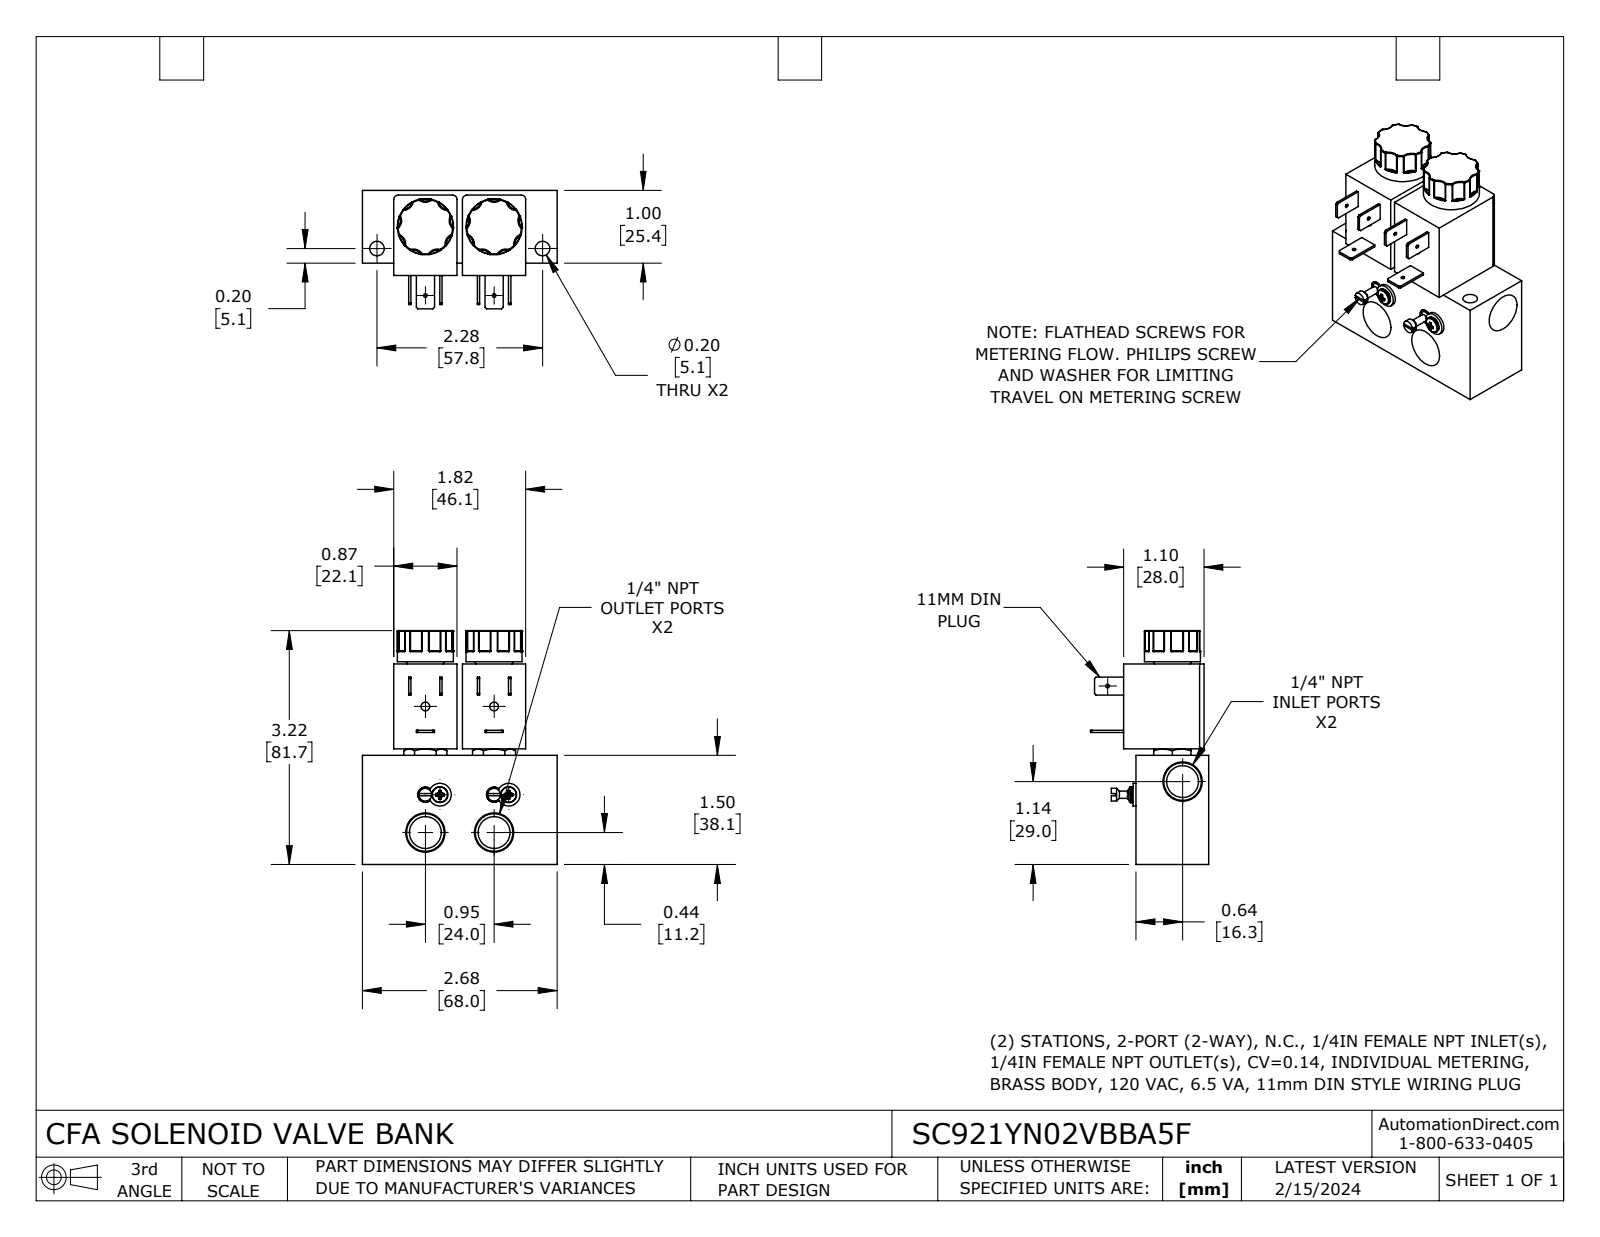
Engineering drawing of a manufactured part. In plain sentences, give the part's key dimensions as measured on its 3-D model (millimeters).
The part is named "SC921YN02VBBA5F". Its 3-D file was written by "SolidWorks 2023 (CONFIG_CONTROL_DESIGN)". It is 1 solid with 589 faces: 156 planar, 152 cylindrical and 281 other. Overall it measures 81.7 by 68 by 41.3 millimeters. Its volume is 100 900 cubic millimeters and its surface area 25 980 square millimeters. Round holes: 3 of diameter 1.3, 3 of diameter 11.1, 2 of diameter 3, 2 of diameter 5.1, 2 of diameter 5.3. Round bosses or shafts: 2 of diameter 19.6, 2 of diameter 7.9, 2 of diameter 5.6, 2 of diameter 5.2, 2 of diameter 4.4, 2 of diameter 2.6, 2 of diameter 2.5. Partial cylindrical surfaces (rounded edges, fillets, slot ends): 36 of radius 0.3, 18 of radius 3.4, 4 of radius 1.5, 1 of radius 7.8. The main face-to-face distances are 25.4, 24, 10.9, 33, 35, 57, 22.1, 38.1, 29.7, 4.3. The hole center spacings are 24, 13.2, 23.6, 27.4, 30.8, 39, 44, 44.1.
